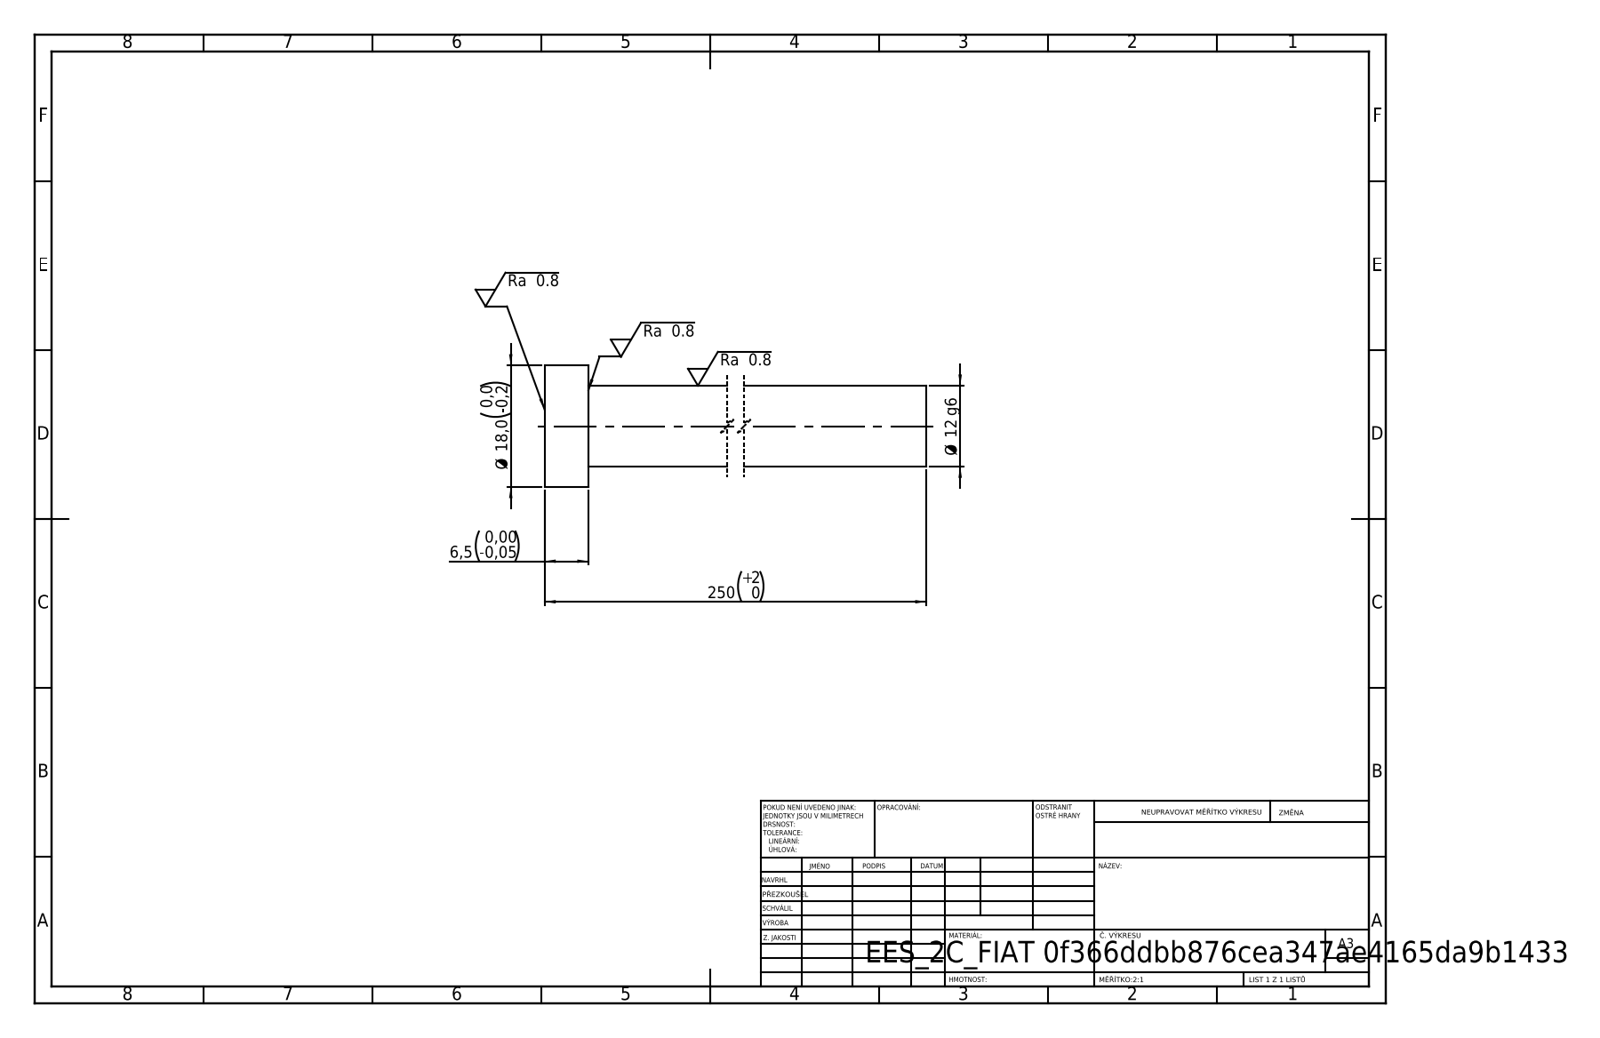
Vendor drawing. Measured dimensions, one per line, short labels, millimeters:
written by: SolidWorks 2019 (CONFIG_CONTROL_DESIGN)
unit: mm
bodies: 1 solid, 7 faces (3 planar, 4 cylindrical, 0 other)
size: 250 × 18 × 18
volume: 29 193 mm³; area: 10 056 mm²
bosses: 1× ⌀18, 1× ⌀12
face distances: 6.5, 250, 243.5
